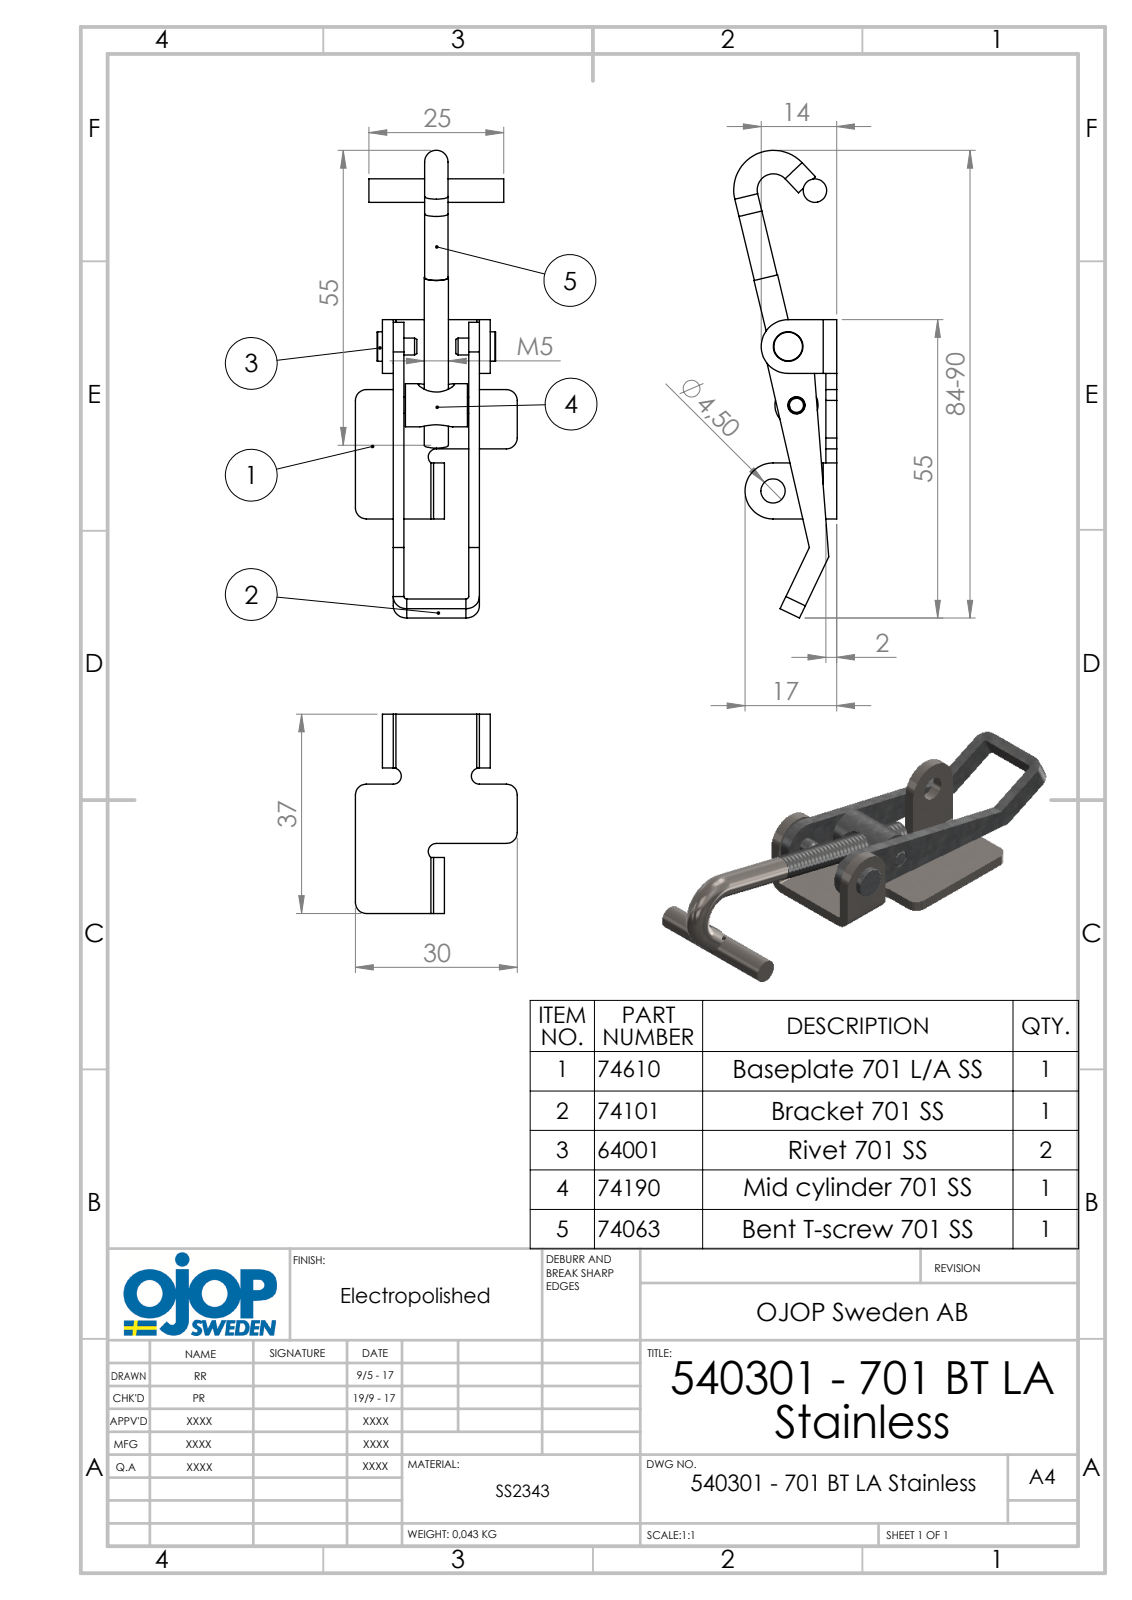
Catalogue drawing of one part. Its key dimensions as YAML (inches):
part_name: "701 - LA; Böjd T-skruv M5_Default<As Machined>; 540301 - 701 TLA RF; 701 - Mid Cylinder (+2 more)"
step_written_by: "SolidWorks 2015 (AUTOMOTIVE_DESIGN)"
units: inches
bodies: {solids: 6, faces: 152, planar: 65, cylindrical: 69, other: 18}
overall_size: [3.507, 1.181, 0.78]
volume: 0.351
surface_area: 10.41
round_holes:
  - {diameter: 0.126, count: 2}
  - {diameter: 0.177, count: 2}
  - {diameter: 0.189, count: 1}
round_bosses_or_shafts:
  - {diameter: 0.197, count: 2}
  - {diameter: 0.315, count: 1}
  - {diameter: 0.217, count: 1}
  - {diameter: 0.197, count: 1}
  - {diameter: 0.172, count: 1}
  - {diameter: 0.124, count: 1}
  - {diameter: 0.118, count: 1}
partial_cylinders:
  - {radius: 0.02, count: 5}
  - {radius: 0.098, count: 5}
  - {radius: 0.079, count: 4}
  - {radius: 0.059, count: 3}
  - {radius: 0.177, count: 1}
  - {radius: 0.197, count: 1}
  - {radius: 0.204, count: 1}
face_to_face_distances: [0.079, 0.551, 0.63, 0.472, 0.256, 0.157, 0.295, 0.374, 0.335, 0.709]
hole_center_spacings: [0.434, 0.649, 1.061]
